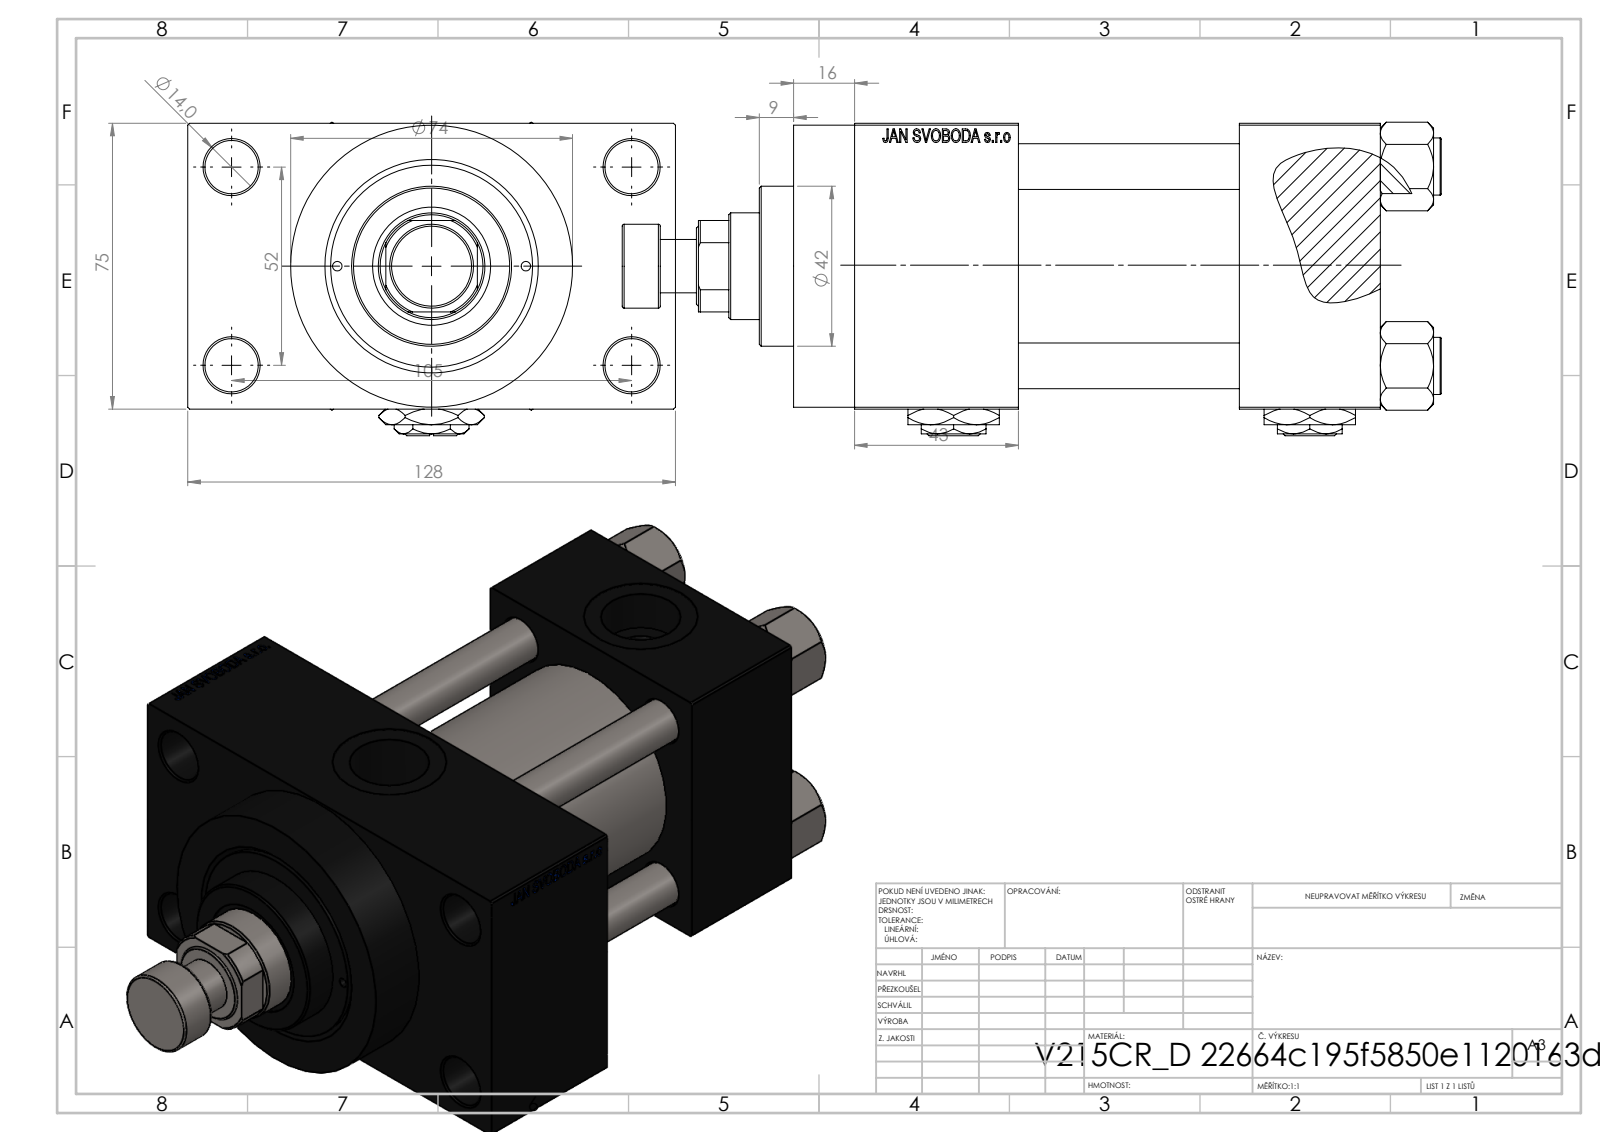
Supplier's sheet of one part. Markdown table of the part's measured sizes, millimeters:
| quantity | value |
| --- | --- |
| part name | V215_VC_A; V215CR_D_Body; V215CR_ROD_END_W; NUT_M5_D (+3 more) |
| STEP written by | SolidWorks 2019 (CONFIG_CONTROL_DESIGN) |
| units | millimeters |
| bodies | 14 solids, 1227 faces (551 planar, 108 cylindrical, 568 other) |
| overall size | 215 × 128 × 82.27 |
| volume | 816 050 mm³ |
| surface area | 175 277 mm² |
| round holes (diameter × count) | 12 × 4, 14 × 4, 2.5 × 2, 7 × 2, 20.96 × 2, 30 × 2, 18.5 × 1, 28 × 1, 31 × 1, 41 × 1, 50 × 1, 53 × 1 |
| round bosses / shafts (diameter × count) | 15 × 4, 74 × 1, 56 × 1, 42 × 1, 22 × 1, 14 × 1 |
| partial cylindrical surfaces (radius × count) | 13.5 × 1 |
| main face-to-face distances | 75, 58, 37, 95, 26.5, 101.5, 138, 101, 43, 16 |
| hole center spacings | 26.19, 26.35, 36.98, 38.03, 52.3, 57.22, 58.43, 58.59 |
